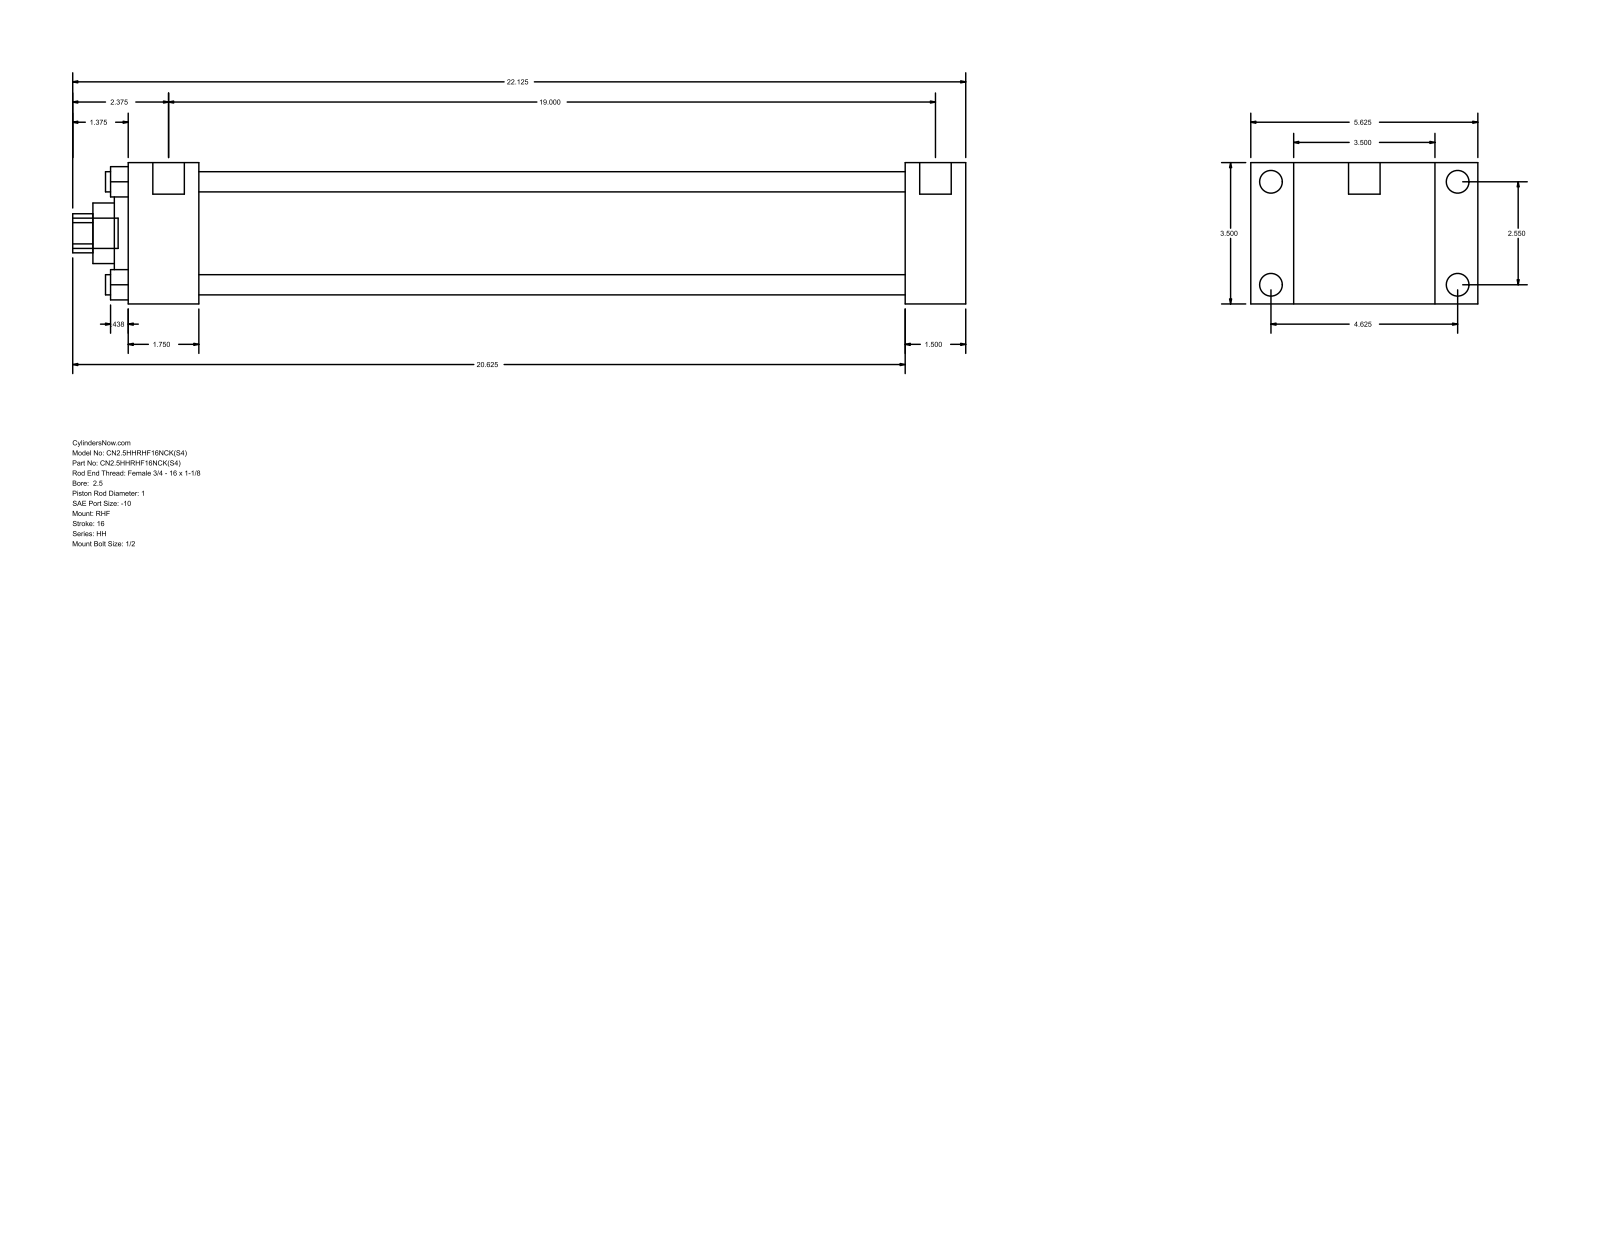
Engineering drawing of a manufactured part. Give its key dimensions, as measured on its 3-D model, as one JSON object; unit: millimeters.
{"part_name": "HH_RHF__0250_1", "step_written_by": "GSSL Pune (CONFIG_CONTROL_DESIGN)", "units": "millimeters", "bodies": {"solids": 0, "faces": 90, "planar": 61, "cylindrical": 29, "other": 0}, "overall_size": [561.98, 142.88, 88.9], "round_holes": [[12.7, 4], [25.4, 1], [38.1, 1], [60.33, 1], [73.03, 1]], "round_bosses_or_shafts": [[14.3, 4], [5.56, 4], [19.84, 2], [19.05, 1]], "partial_cylinders_radius": [[12.29, 1]], "face_to_face_distances": [88.9, 38.1, 26.99, 115.89, 488.96, 527.06, 142.88, 44.46, 444.5, 482.6], "hole_center_spacings": [45.79, 64.76, 91.58]}
